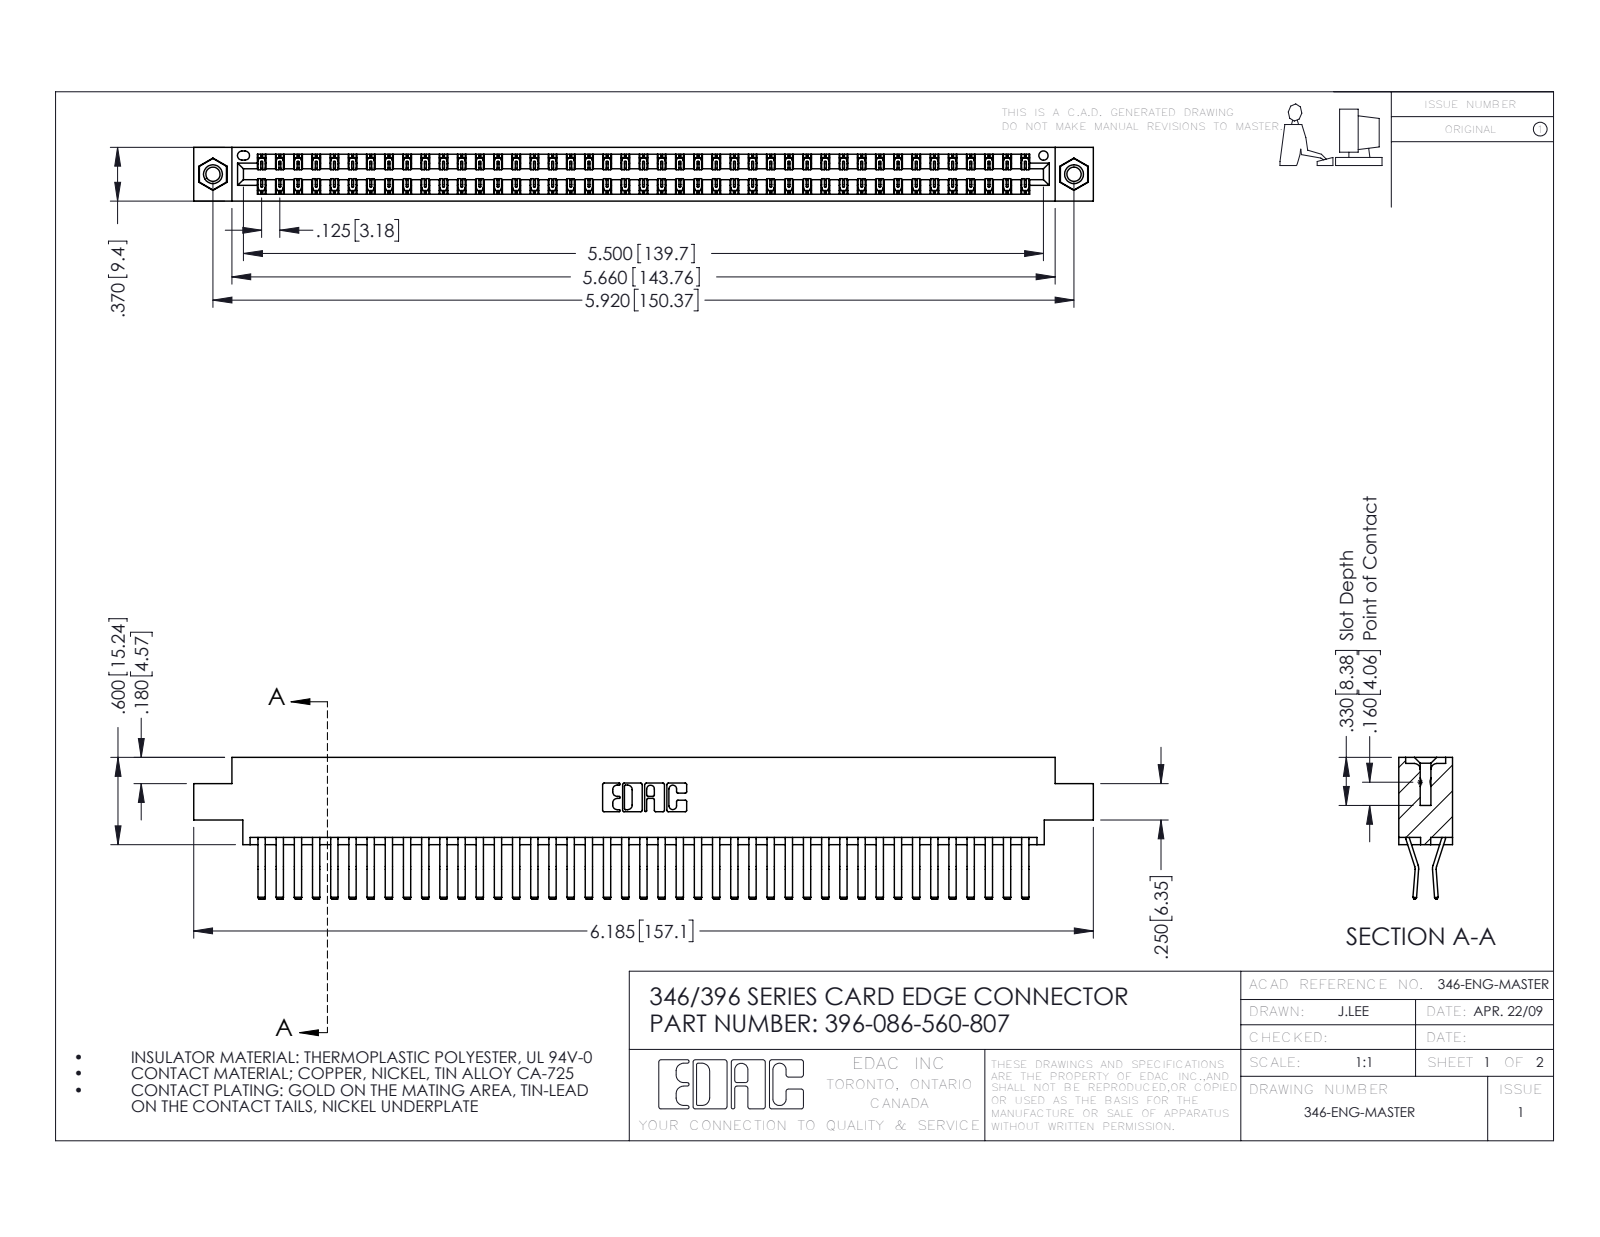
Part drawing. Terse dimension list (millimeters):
name: 345-250-001_345-250-005-103; 396-086-560-807; 345-292-001_560 Tail; 346 Part_0.170 Offset - 0.156 Dia-TI
written by: SolidWorks 2016 (CONFIG_CONTROL_DESIGN)
unit: mm
bodies: 89 solids, 4830 faces (3122 planar, 1692 cylindrical, 16 other)
size: 157.1 × 24.8 × 9.4
volume: 15 700 mm³; area: 23 340 mm²
holes: 2× ⌀2.5, 2× ⌀3.2, 2× ⌀4, 1× ⌀1.6
bosses: 2× ⌀3.9
rounds: 129× R0.2, 22× R0.3, 6× R0.2, 6× R0.8, 3× R0.7, 2× R0.3, 2× R0.4, 2× R0.6
face distances: 1.2, 8.2, 9.4, 0.6, 6.4, 1.8, 7.6, 7, 5.6, 3.8
hole spacings: 6.2, 145.1, 150.4
